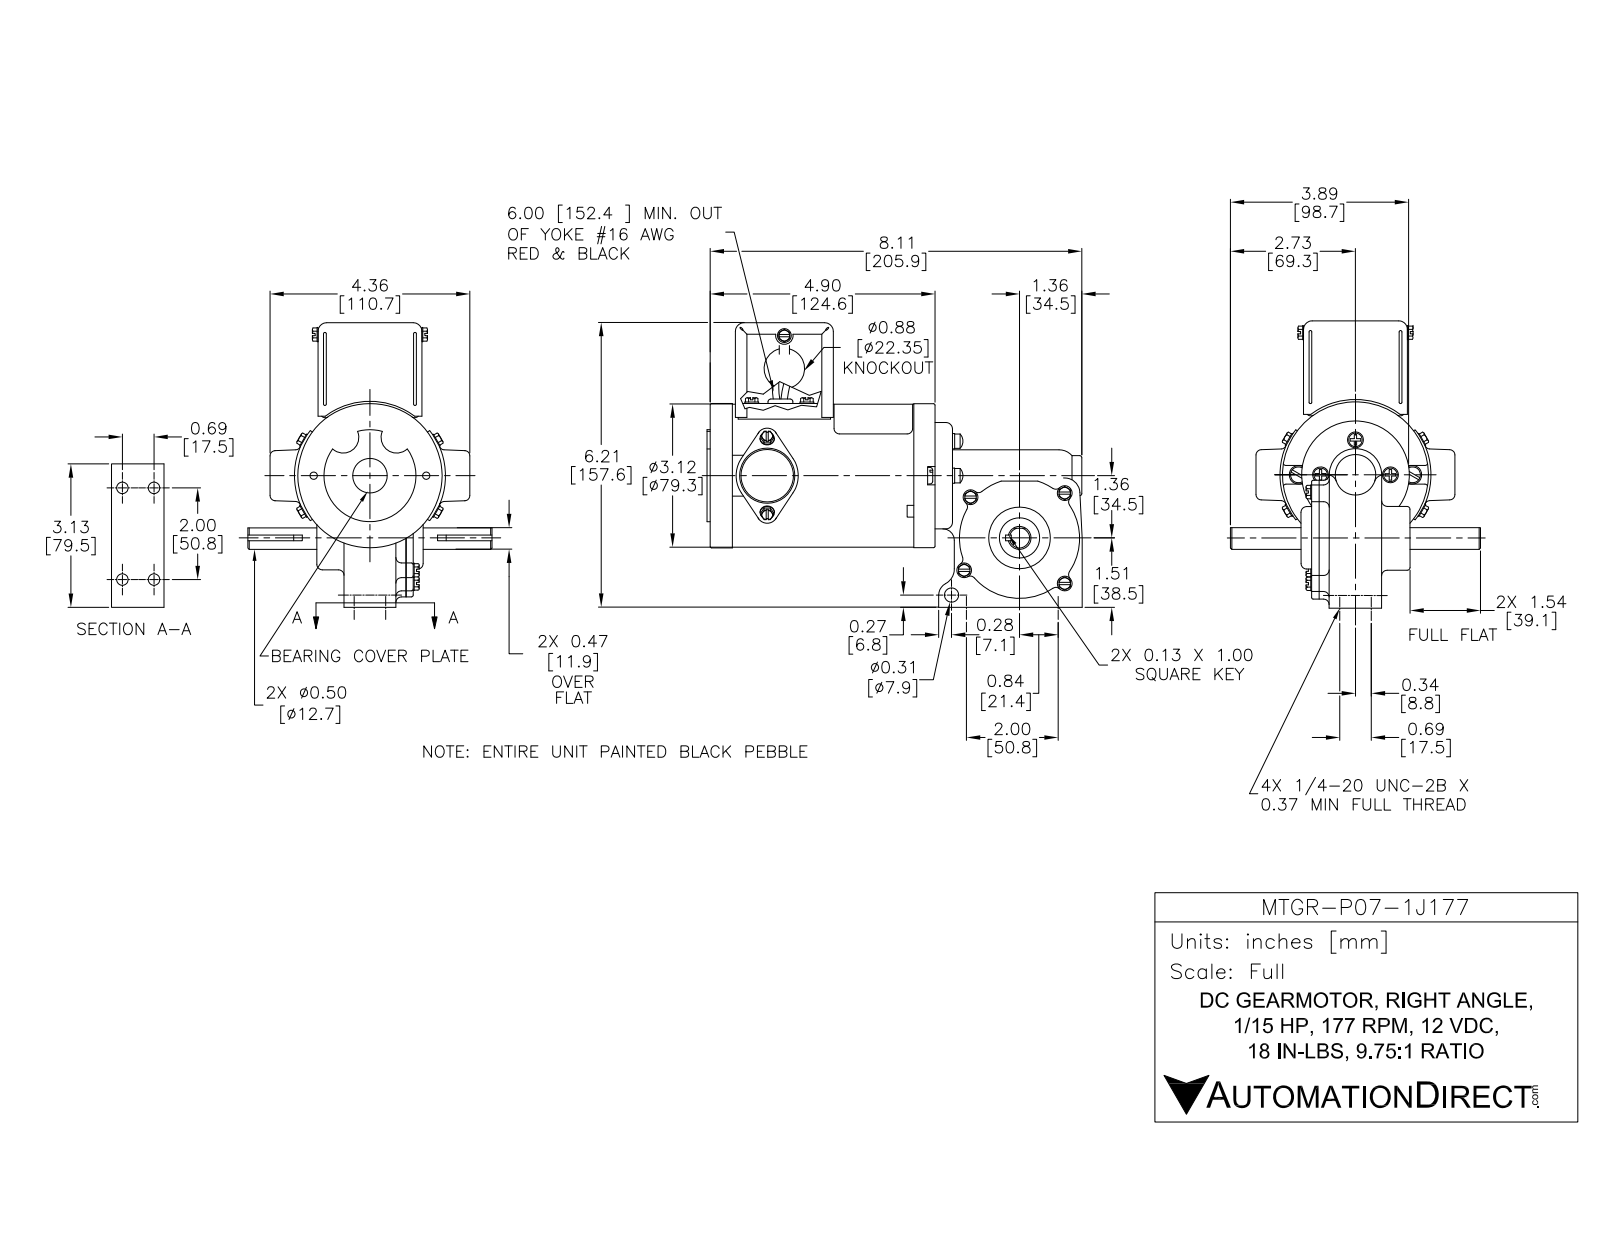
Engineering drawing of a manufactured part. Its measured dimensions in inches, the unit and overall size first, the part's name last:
Units: inches
Overall size (bounding box): 8.179 × 6.274 × 5.453
Round holes (diameter × count): ⌀0.25 ×5, ⌀0.094 ×2, ⌀0.198 ×2, ⌀0.3 ×1, ⌀0.301 ×1, ⌀0.375 ×1, ⌀0.5 ×1, ⌀0.86 ×1, ⌀1.225 ×1, ⌀3 ×1, ⌀3.125 ×1
Round bosses / shafts (diameter × count): ⌀0.321 ×4, ⌀0.3 ×4, ⌀0.346 ×3, ⌀0.295 ×3, ⌀0.125 ×2, ⌀0.1 ×2, ⌀3.156 ×1, ⌀3.14 ×1
Partial cylindrical surfaces — rounded edges, fillets, slot ends (radius × count): R0.1 ×10, R0.191 ×4, R0.234 ×4, R0.15 ×2, R0.159 ×2, R0.341 ×2, R0.25 ×1, R0.34 ×1
Main face-to-face distances: 0.031, 0.25, 0.063, 4.65, 2.135, 0.307, 2.047, 1.67, 1.608, 0.245
Hole centre spacings: 0.343, 0.456, 0.686, 1.23, 2, 2.029, 2.114, 2.326
Volume: 27.37 in³ · Surface area: 297.1 in²
Bodies: 40 solids, 712 faces (436 planar, 210 cylindrical, 66 other)
Part name (STEP PRODUCT): P07-1J177
STEP written by: SolidWorks 2013 (AUTOMOTIVE_DESIGN)
